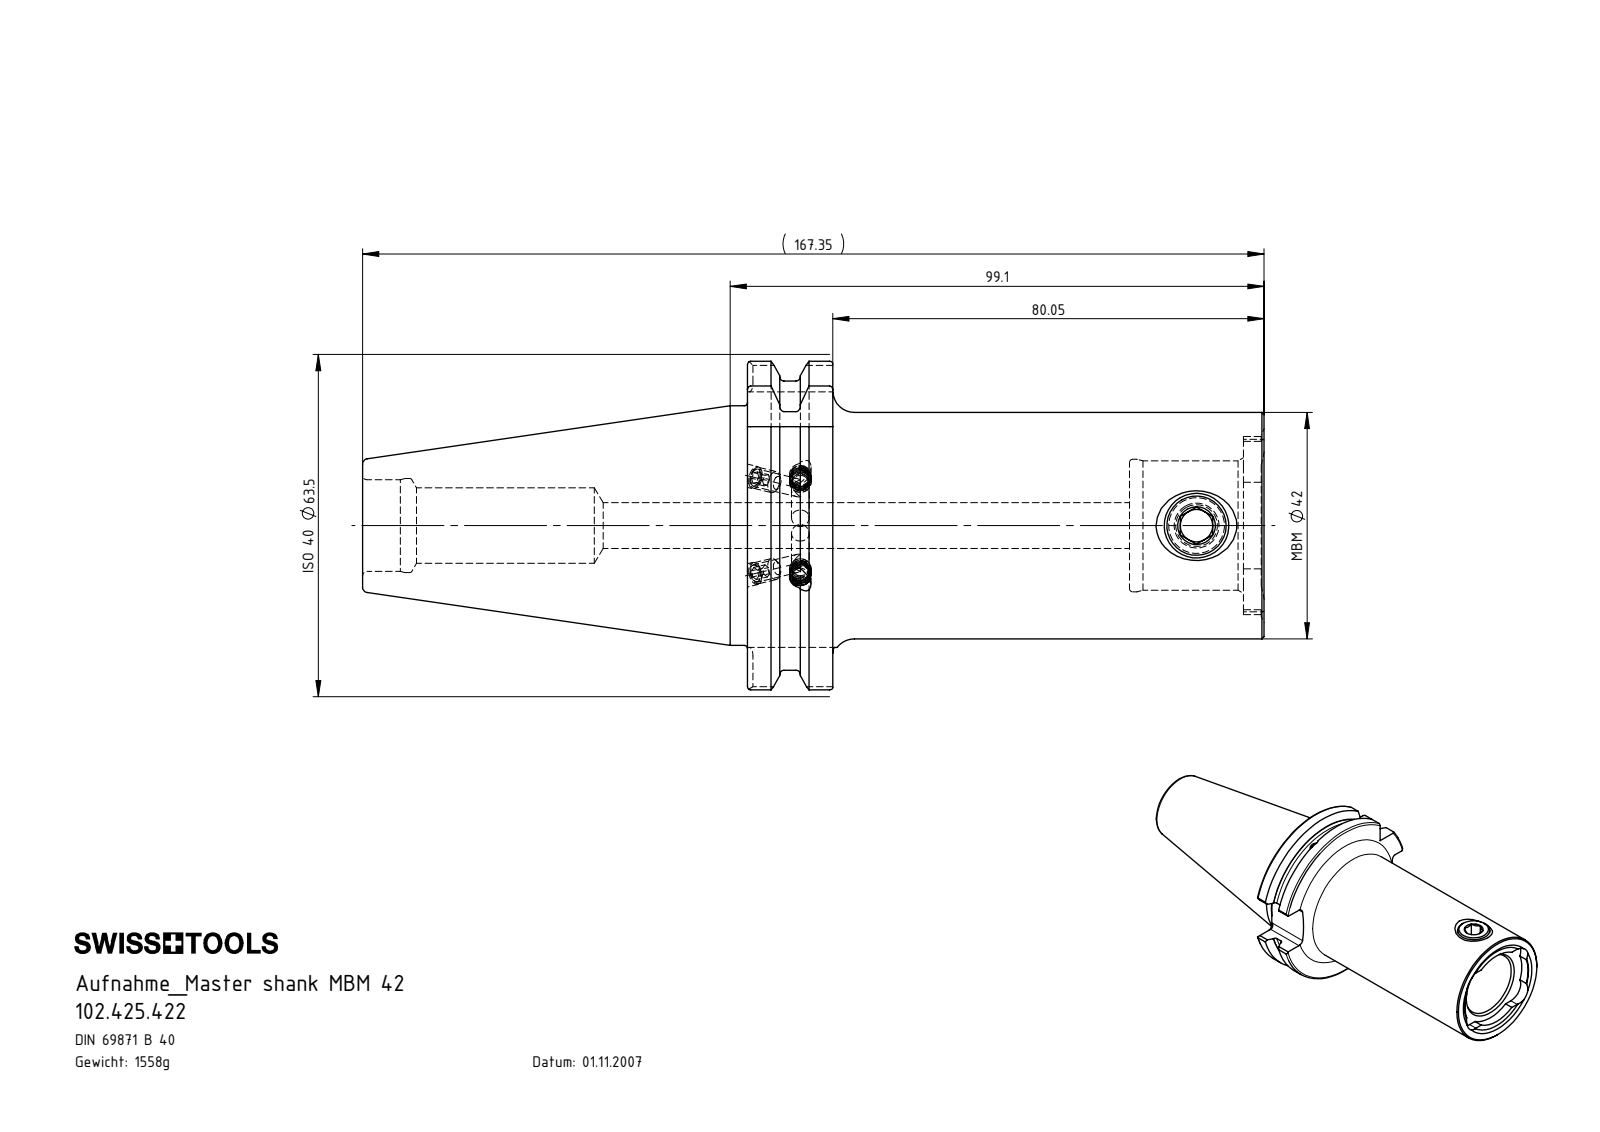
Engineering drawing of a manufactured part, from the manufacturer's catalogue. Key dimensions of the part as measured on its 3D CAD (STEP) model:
Part name (STEP PRODUCT): KVT_MB_600_040; MB4-ER1.001.013_A; SB4-MB4.K01.099_D_mit Bundkhlung; 102.425.422 (+1 more)
STEP written by: SolidWorks 2017 (CONFIG_CONTROL_DESIGN)
Units: millimetres
Bodies: 8 solids, 303 faces (80 planar, 88 cylindrical, 135 other)
Overall size (bounding box): 167.35 × 63.5 × 60.94
Volume: 198 460 mm³ · Surface area: 35 216 mm²
Round holes (diameter × count): ⌀3.3 ×3, ⌀3 ×2, ⌀4.2 ×2, ⌀4 ×1, ⌀6 ×1, ⌀8.5 ×1, ⌀11 ×1, ⌀14 ×1, ⌀17 ×1, ⌀17.45 ×1, ⌀24 ×1, ⌀24.6 ×1
Round bosses / shafts (diameter × count): ⌀4 ×4, ⌀44.45 ×1, ⌀42 ×1, ⌀12 ×1
Partial cylindrical surfaces — rounded edges, fillets, slot ends (radius × count): R1.6 ×8, R5.2 ×4, R14.9 ×1, R16.52 ×1, R28 ×1, R31.75 ×1
Main face-to-face distances: 15.85, 70.9, 55.05, 92.05, 76.2, 21.15, 3.85, 95.9, 80.05, 25
